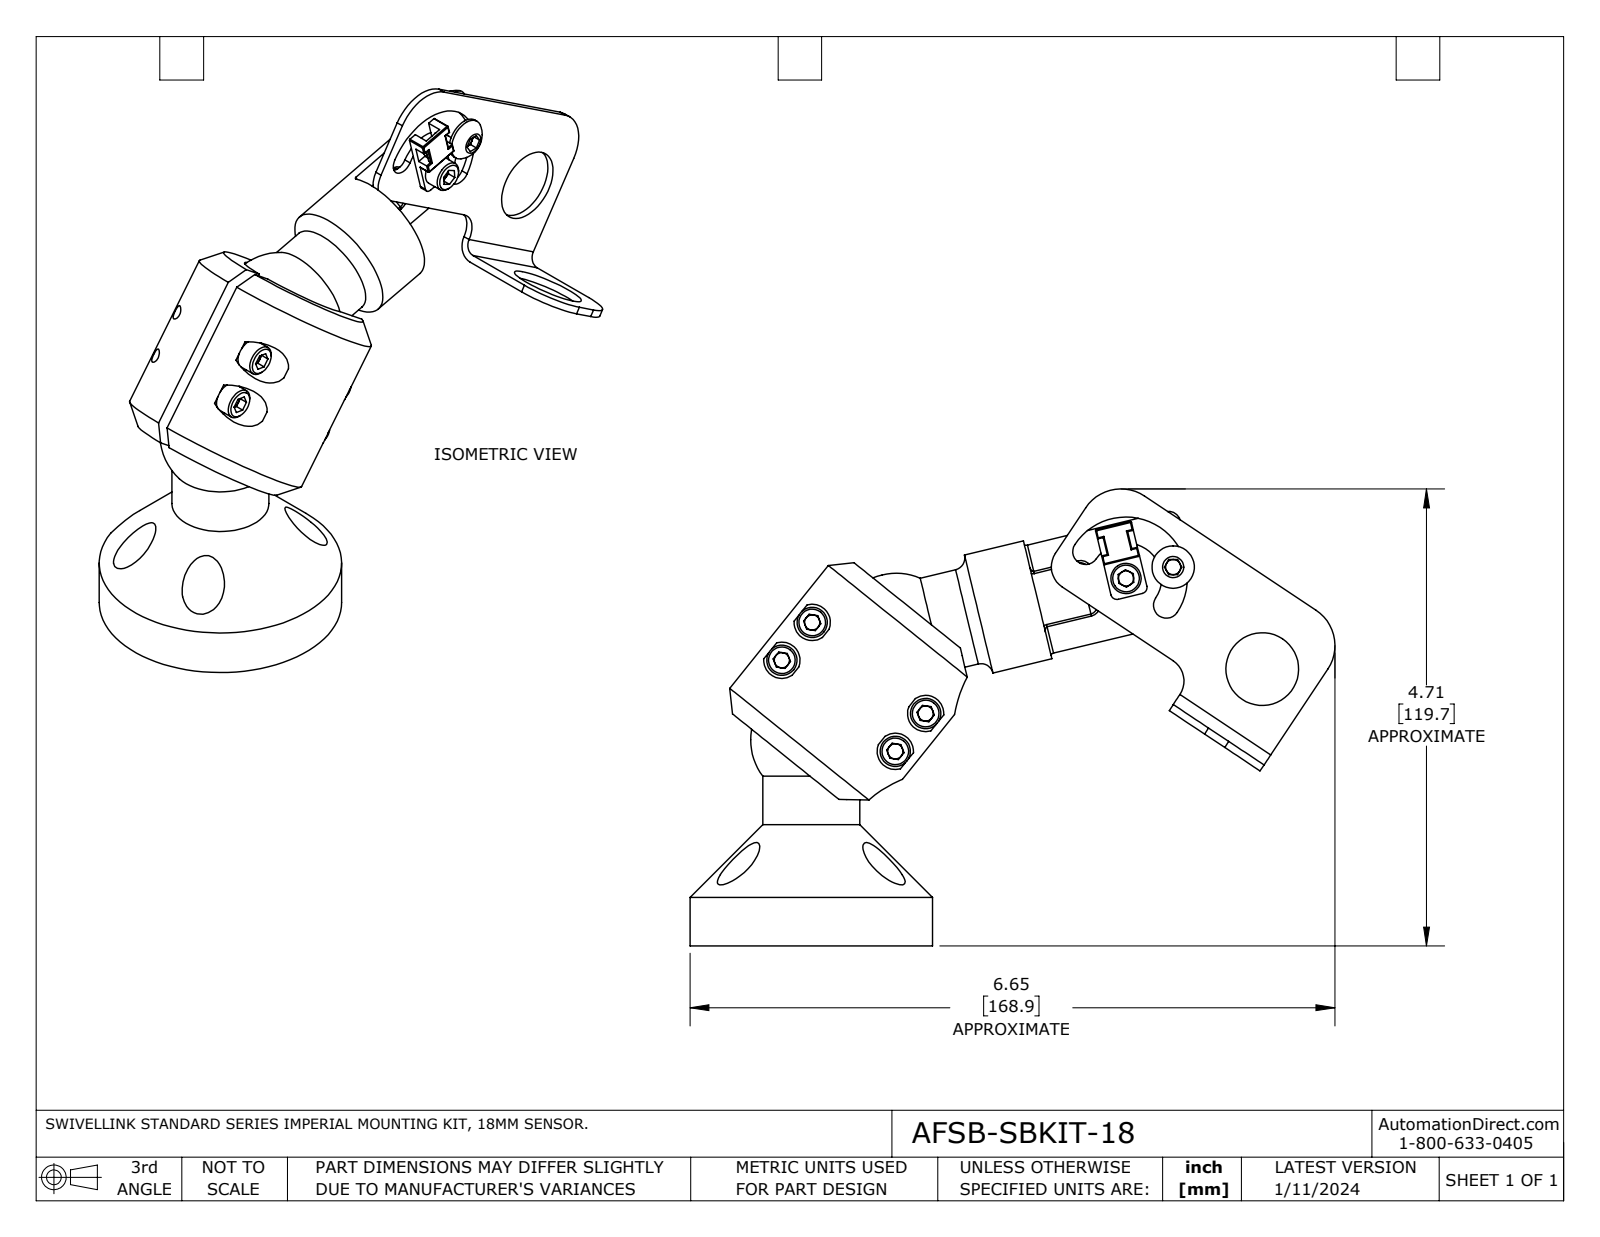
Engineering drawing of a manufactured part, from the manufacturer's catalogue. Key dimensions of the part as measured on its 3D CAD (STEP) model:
Part name (STEP PRODUCT): AFSB-SBKIT-18
STEP written by: SolidWorks 2023 (AUTOMOTIVE_DESIGN)
Units: inches
Bodies: 12 solids, 294 faces (155 planar, 89 cylindrical, 50 other)
Overall size (bounding box): 6.65 × 4.741 × 2.425
Volume: 6.53 in³ · Surface area: 84.39 in²
Round holes (diameter × count): ⌀0.15 ×5, ⌀0.221 ×4, ⌀0.281 ×4, ⌀0.437 ×4, ⌀0.75 ×3, ⌀0.375 ×2, ⌀0.375 ×2, ⌀0.2 ×1, ⌀0.201 ×1, ⌀0.281 ×1, ⌀0.875 ×1, ⌀1.125 ×1
Round bosses / shafts (diameter × count): ⌀0.313 ×5, ⌀0.19 ×5, ⌀1 ×2, ⌀2.5 ×1, ⌀1.98 ×1, ⌀1.25 ×1, ⌀0.437 ×1, ⌀0.25 ×1
Partial cylindrical surfaces — rounded edges, fillets, slot ends (radius × count): R0.01 ×12, R0.437 ×4, R0.063 ×2, R0.133 ×2, R0.25 ×2, R0.525 ×2, R0.562 ×2, R0.03 ×1
Main face-to-face distances: 0.074, 0.125, 0.113, 0.187, 0.238, 0.312, 0.075, 2, 0.341, 0.465
Hole centre spacings: 0.902, 0.5, 1.5, 1, 1.581, 1.803, 1.397, 1.5
